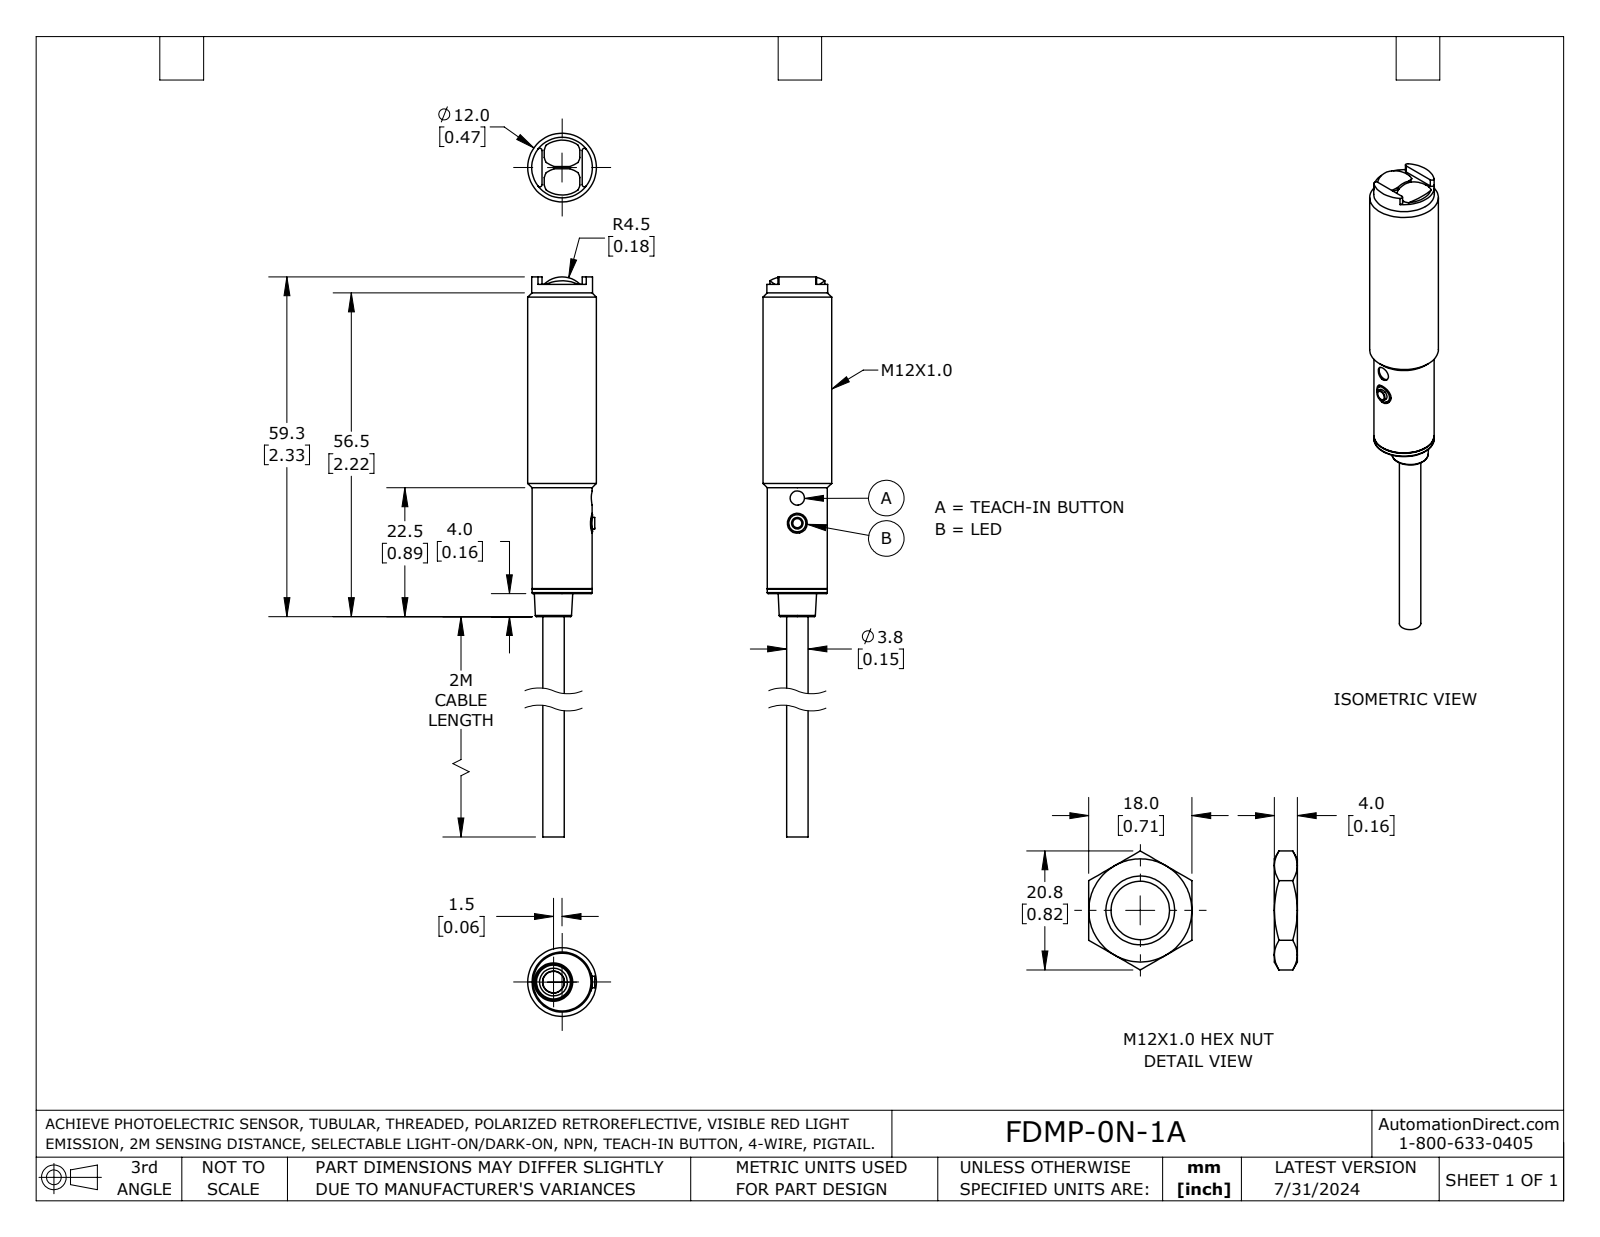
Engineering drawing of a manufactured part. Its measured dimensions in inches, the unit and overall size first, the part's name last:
Units: inches
Overall size (bounding box): 3.752 × 0.472 × 0.472
Round holes (diameter × count): ⌀0.098 ×1, ⌀0.138 ×1, ⌀0.152 ×1
Round bosses / shafts (diameter × count): ⌀0.472 ×1, ⌀0.417 ×1, ⌀0.413 ×1, ⌀0.148 ×1, ⌀0.118 ×1, ⌀0.079 ×1
Partial cylindrical surfaces — rounded edges, fillets, slot ends (radius × count): R0.016 ×4, R0.189 ×3, R0.193 ×1
Main face-to-face distances: 2.126, 2.177, 0.051, 1.575, 3.701, 3.752, 1.417, 0.157, 2.283, 2.335
Hole centre spacings: 0.173
Volume: 0.375 in³ · Surface area: 4.341 in²
Bodies: 1 solid, 51 faces (19 planar, 22 cylindrical, 10 other)
Part name (STEP PRODUCT): DMP_1A_fig
STEP written by: SolidWorks 2023 (AUTOMOTIVE_DESIGN)
